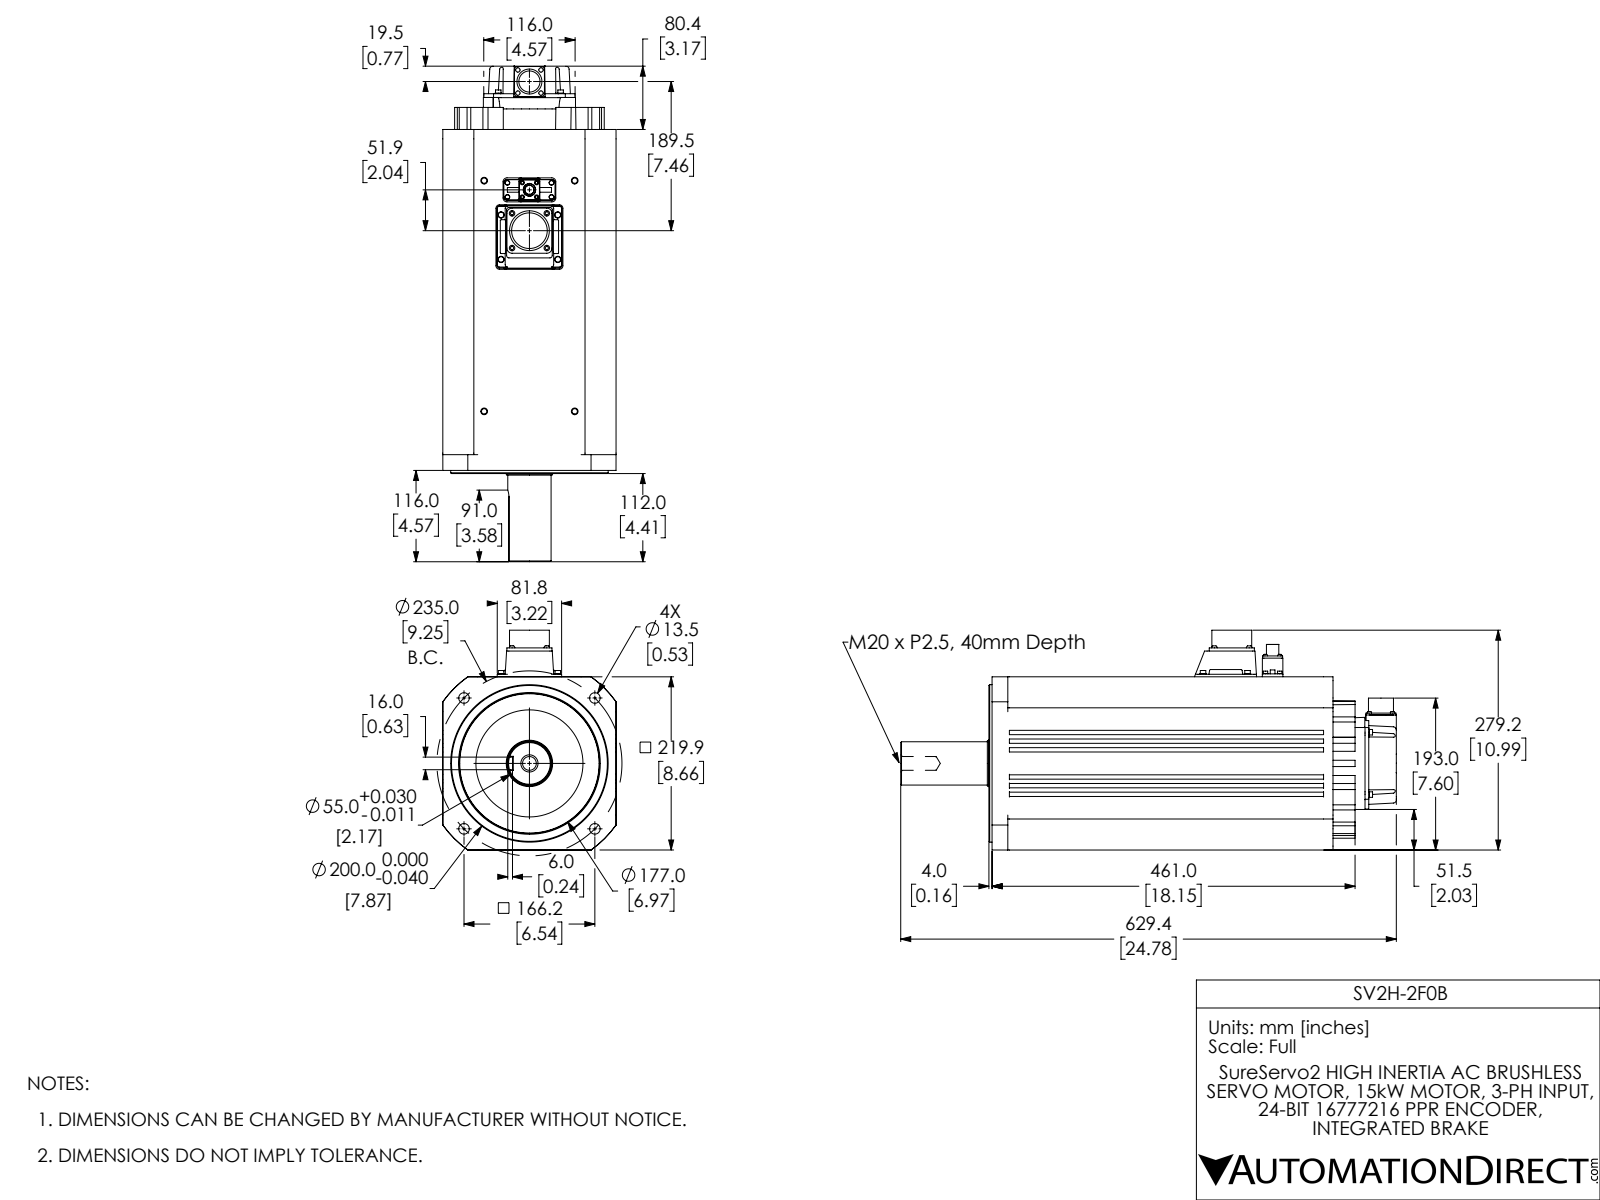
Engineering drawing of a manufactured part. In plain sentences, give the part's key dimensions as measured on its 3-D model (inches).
The part is named "SV2H-2F0B 1d r1b". Its 3-D file was written by "SolidWorks 2017 (AUTOMOTIVE_DESIGN)". It is 2 solids with 829 faces: 392 planar, 283 cylindrical and 154 other. Overall it measures 24.784 by 10.992 by 8.661 inches. Its volume is 1 197 cubic inches and its surface area 1 049 square inches. Round holes: 4 of diameter 0.169, 4 of diameter 0.181, 4 of diameter 0.268, 4 of diameter 0.531, 1 of diameter 0.461, 1 of diameter 0.689, 1 of diameter 1.058, 1 of diameter 1.783, 1 of diameter 7.087. Round bosses or shafts: 8 of diameter 0.315, 8 of diameter 0.276, 4 of diameter 0.236, 4 of diameter 0.217, 4 of diameter 0.157, 1 of diameter 7.874, 1 of diameter 7.008, 1 of diameter 5.354. Partial cylindrical surfaces (rounded edges, fillets, slot ends): 28 of radius 0.197, 24 of radius 0.031, 22 of radius 0.02, 16 of radius 0.157, 14 of radius 0.118, 7 of radius 0.118, 4 of radius 0.039, 4 of radius 0.079. The main face-to-face distances are 8.661, 1.551, 7.11, 0.217, 0.433, 5.559, 2.441, 2.657, 0.65, 2.224. The hole center spacings are 4.626, 6.543, 1.621, 1.893, 1.912, 2.019, 2.224, 2.31.
